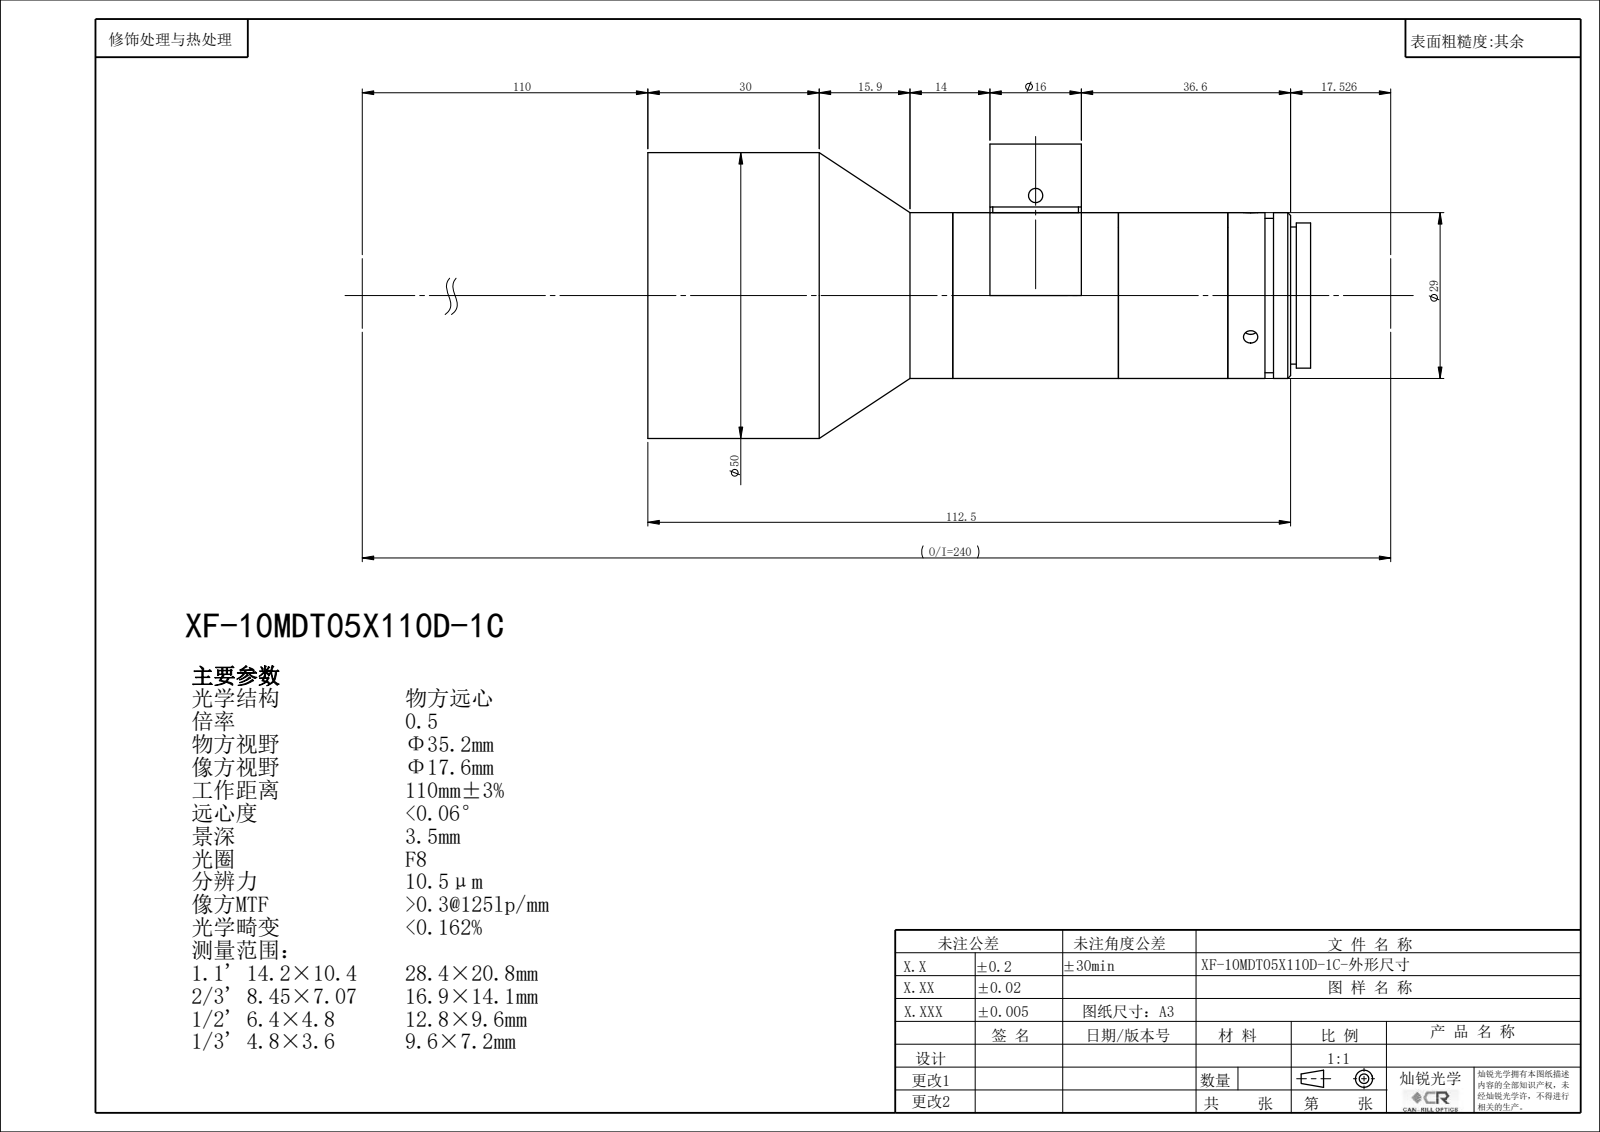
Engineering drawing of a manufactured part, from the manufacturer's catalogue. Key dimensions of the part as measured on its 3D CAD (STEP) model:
Part name (STEP PRODUCT): XF-10MDT05X110D-1C
STEP written by: SolidWorks 2014 (CONFIG_CONTROL_DESIGN)
Units: millimetres
Bodies: 0 solids, 120 faces (49 planar, 61 cylindrical, 10 other)
Overall size (bounding box): 116.03 × 51.5 × 50
Round holes (diameter × count): ⌀1.6 ×4, ⌀2.2 ×4, ⌀2.5 ×4, ⌀8 ×1, ⌀14 ×1, ⌀15.5 ×1, ⌀17.4 ×1, ⌀20 ×1, ⌀21.4 ×1, ⌀42 ×1, ⌀46 ×1
Round bosses / shafts (diameter × count): ⌀50 ×1, ⌀29 ×1, ⌀27 ×1, ⌀25.4 ×1, ⌀24 ×1, ⌀16 ×1
Main face-to-face distances: 6.5, 1, 29, 101.53, 22.5, 33.65, 48.15, 4.17, 97.36, 11
Hole centre spacings: 11.66, 12, 20, 23.32, 33.19, 44.78, 37.65
